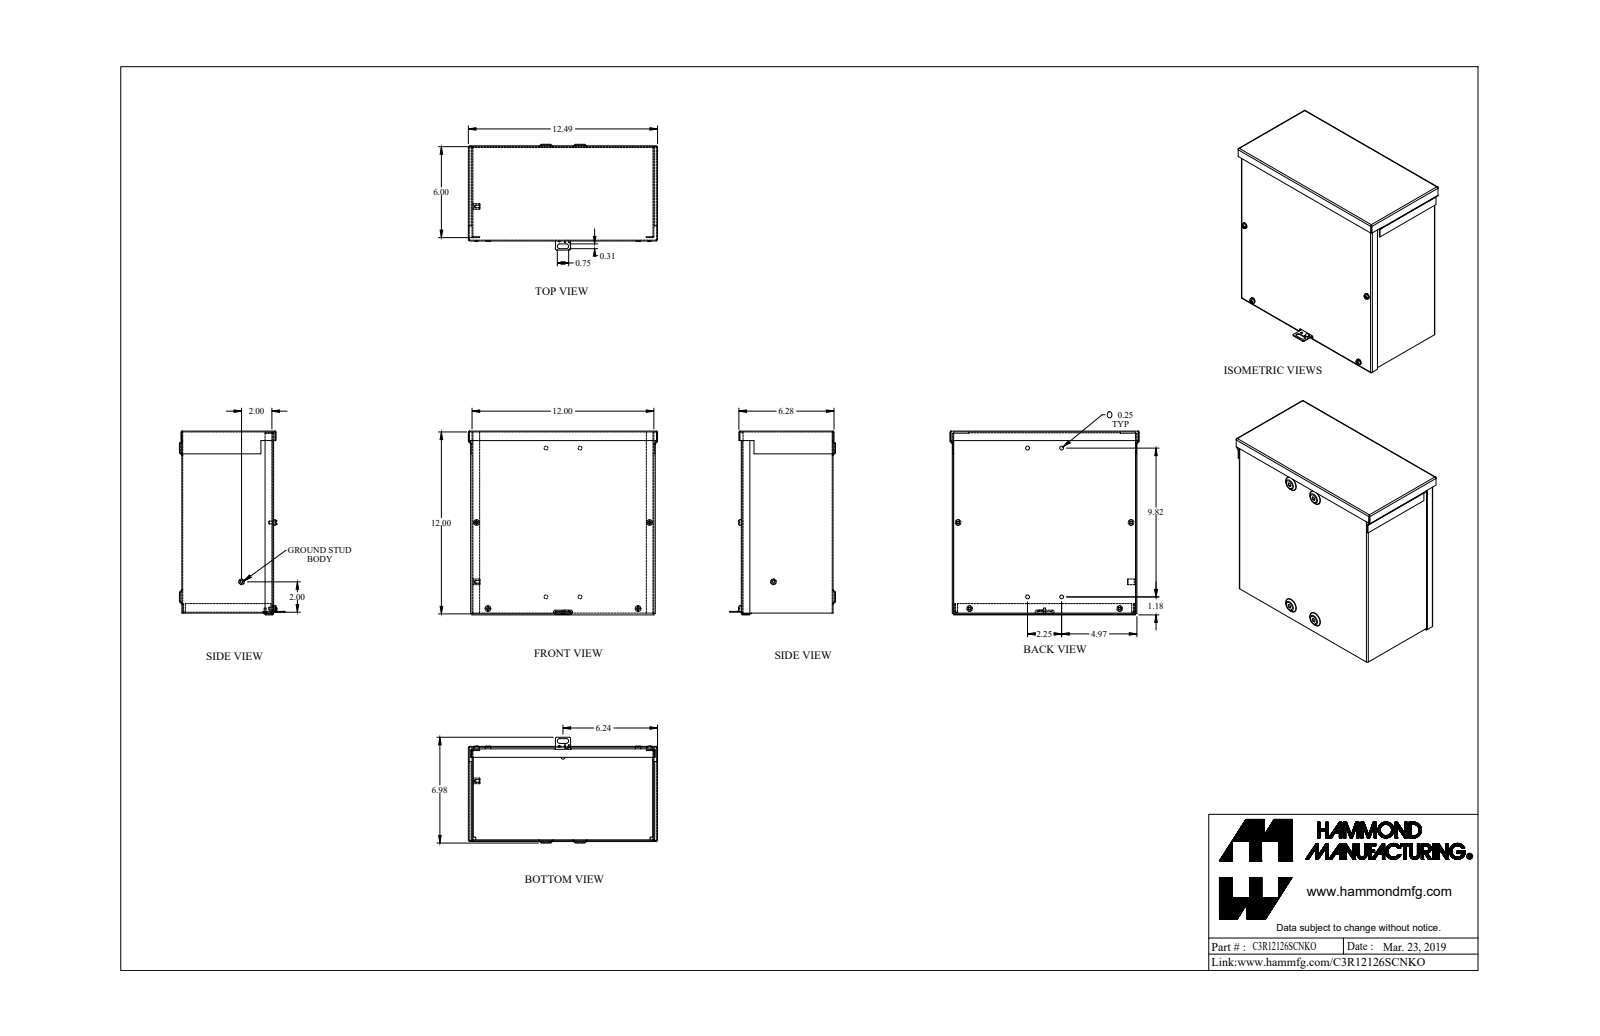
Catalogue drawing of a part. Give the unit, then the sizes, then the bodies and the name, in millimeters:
Units: millimetres
Overall size (bounding box): 317.2 × 307.8 × 177.2
Round holes (diameter × count): ⌀4.3 ×4, ⌀6.4 ×4, ⌀3.2 ×1, ⌀3.5 ×1, ⌀4 ×1
Round bosses / shafts (diameter × count): ⌀4.8 ×4, ⌀9.5 ×3, ⌀9.5 ×2, ⌀3.2 ×1
Partial cylindrical surfaces — rounded edges, fillets, slot ends (radius × count): R0.7 ×21, R2.2 ×21, R2.8 ×8, R3.2 ×8, R4 ×2
Main face-to-face distances: 1.4, 152.4, 303.4, 151, 153.8, 304.8, 1.4, 301.9, 301.9, 303.4
Hole centre spacings: 170.6, 213.7, 57.2, 99.2, 145.5, 155.6, 249.4, 255.8
Volume: 618 300 mm³ · Surface area: 861 900 mm²
Bodies: 11 solids, 404 faces (211 planar, 107 cylindrical, 86 other)
Part name (STEP PRODUCT): C3R12126SCNKO_Default
STEP written by: SolidWorks 2019 (CONFIG_CONTROL_DESIGN)
